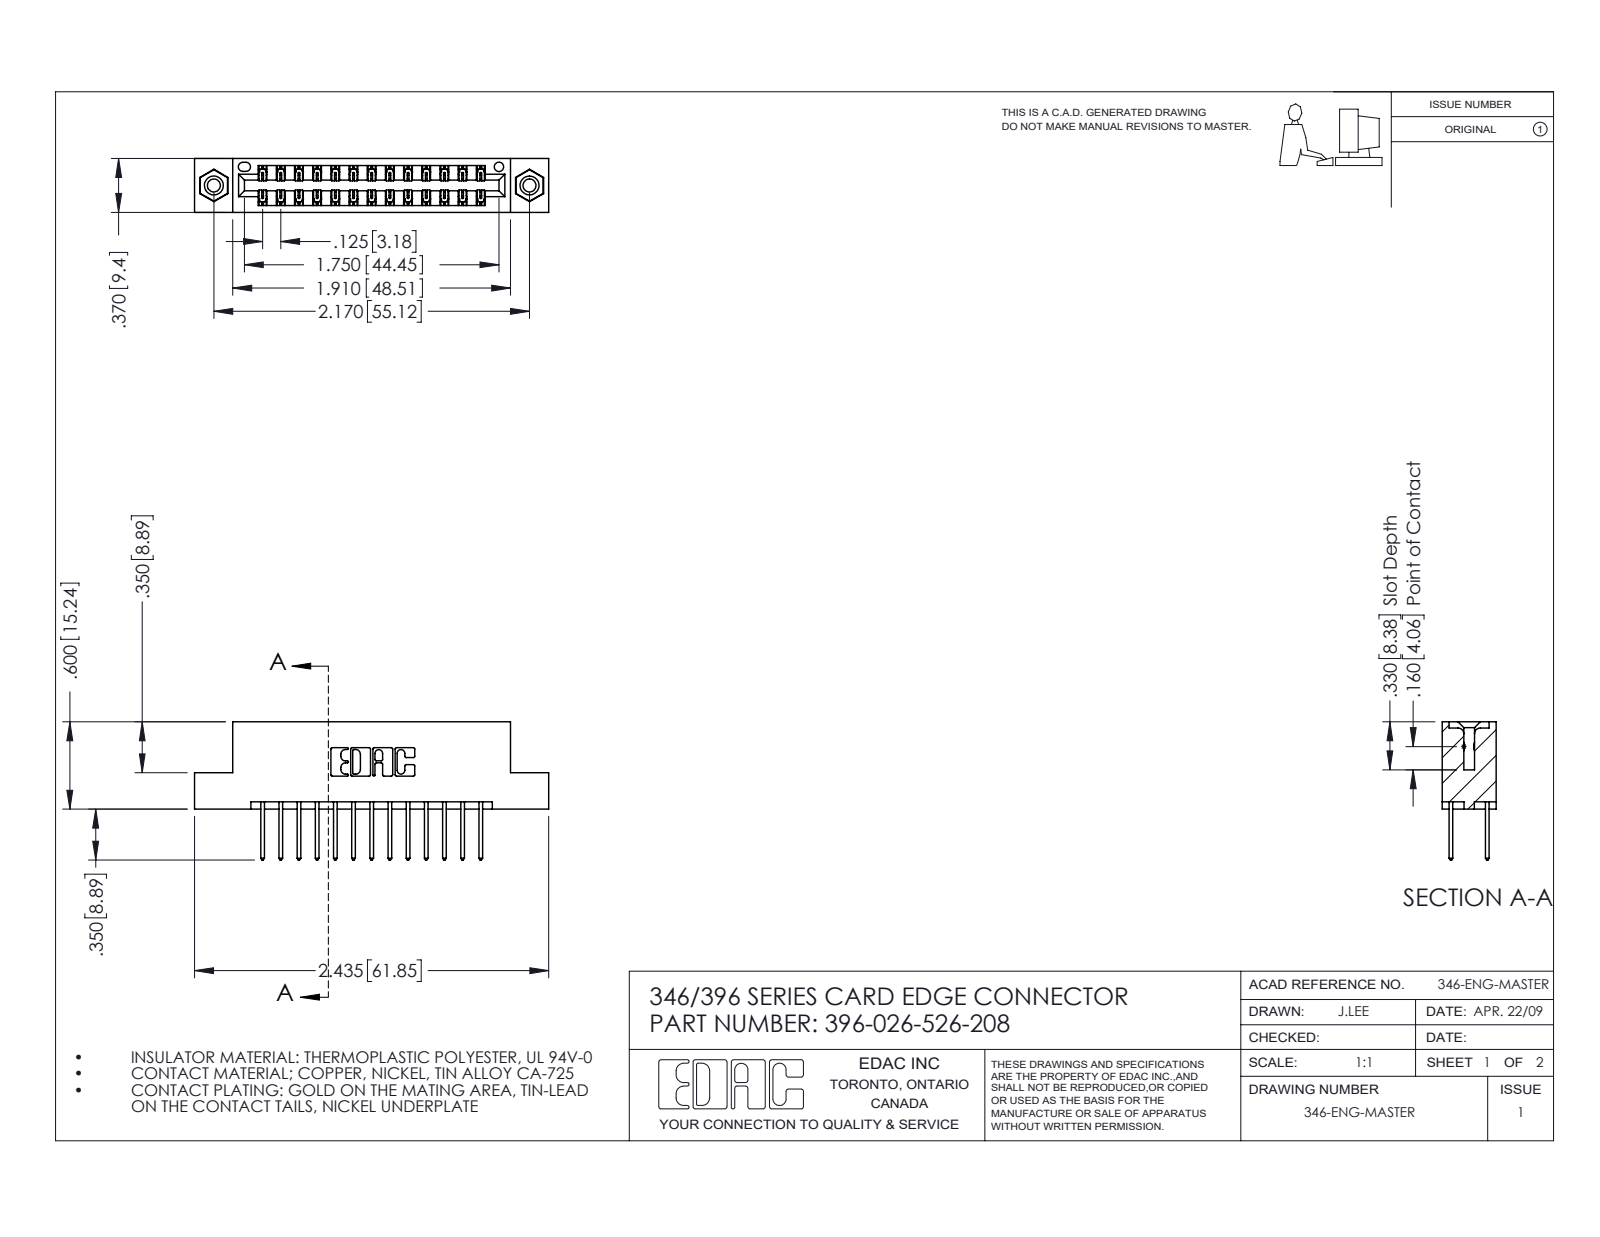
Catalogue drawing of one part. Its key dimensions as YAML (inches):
part_name: "345-292-001_345-293-126; 396-026-526-208; 345-250-001_345-250-003-102; 346 Part_Flush Mounting Lugs - 0.156 Dia-TI"
step_written_by: "SolidWorks 2016 (CONFIG_CONTROL_DESIGN)"
units: inches
bodies: {solids: 29, faces: 1534, planar: 1018, cylindrical: 500, other: 16}
overall_size: [2.435, 0.95, 0.37]
volume: 0.356
surface_area: 12.07
round_holes:
  - {diameter: 0.089, count: 2}
  - {diameter: 0.125, count: 2}
  - {diameter: 0.156, count: 2}
  - {diameter: 0.064, count: 1}
round_bosses_or_shafts:
  - {diameter: 0.155, count: 2}
partial_cylinders:
  - {radius: 0.006, count: 39}
  - {radius: 0.01, count: 26}
  - {radius: 0.01, count: 22}
  - {radius: 0.007, count: 6}
  - {radius: 0.031, count: 6}
  - {radius: 0.026, count: 3}
  - {radius: 0.014, count: 2}
  - {radius: 0.022, count: 2}
face_to_face_distances: [0.25, 0.048, 0.322, 0.37, 0.072, 0.298, 0.025, 0.275, 0.148, 0.222]
hole_center_spacings: [0.246, 1.964, 2.17]
